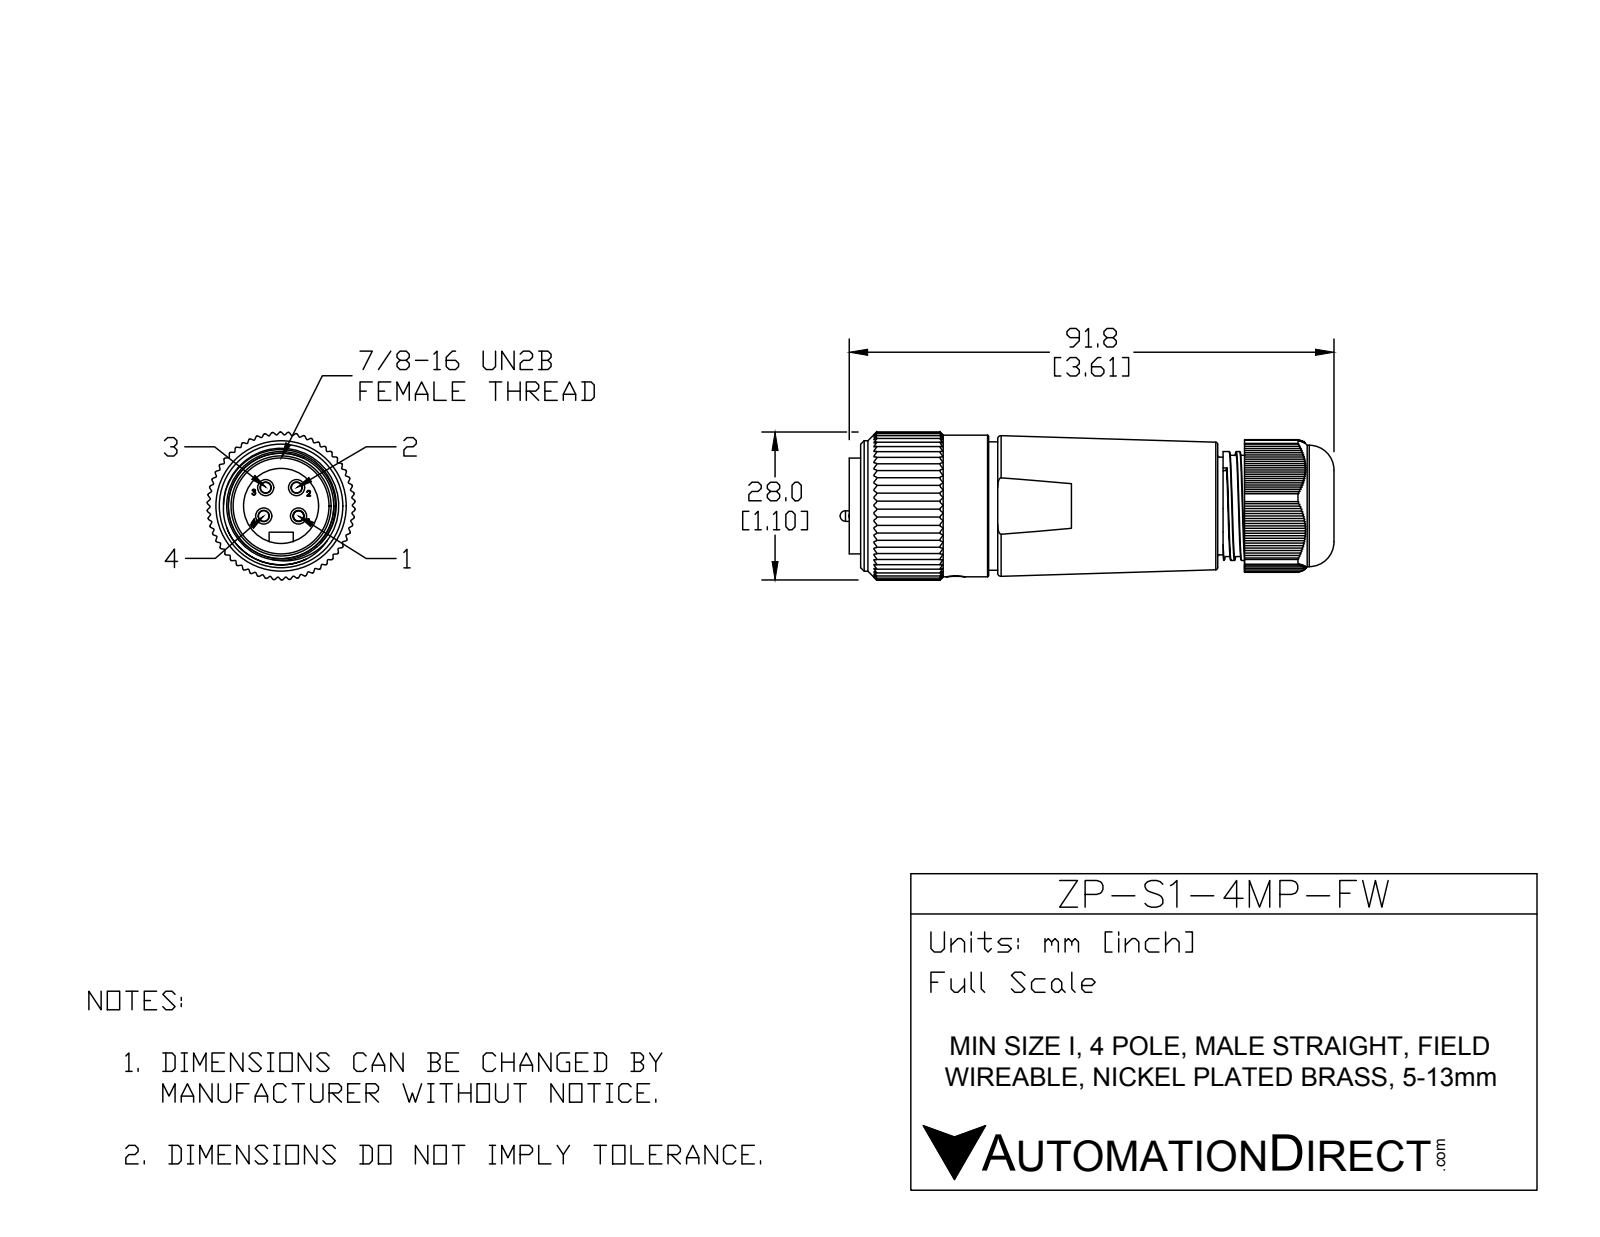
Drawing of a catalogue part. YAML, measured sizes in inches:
part_name: "MIN-4MP-FW"
step_written_by: "SolidWorks 2015 (AUTOMOTIVE_DESIGN)"
units: inches
bodies: {solids: 1, faces: 855, planar: 461, cylindrical: 324, other: 70}
overall_size: [3.681, 1.102, 1.102]
volume: 2.634
surface_area: 19
round_holes:
  - {diameter: 0.138, count: 1}
  - {diameter: 0.53, count: 1}
  - {diameter: 0.56, count: 1}
  - {diameter: 0.81, count: 1}
  - {diameter: 1, count: 1}
round_bosses_or_shafts:
  - {diameter: 0.12, count: 4}
  - {diameter: 0.079, count: 4}
  - {diameter: 1.055, count: 1}
  - {diameter: 0.972, count: 1}
  - {diameter: 0.957, count: 1}
  - {diameter: 0.945, count: 1}
  - {diameter: 0.905, count: 1}
  - {diameter: 0.811, count: 1}
partial_cylinders:
  - {radius: 0.01, count: 116}
  - {radius: 0.008, count: 58}
  - {radius: 0.09, count: 1}
  - {radius: 0.521, count: 1}
  - {radius: 0.551, count: 1}
face_to_face_distances: [0.014, 0.028, 0.043, 0.057, 0.652, 0.071, 0.746, 0.666, 0.638, 0.68]
